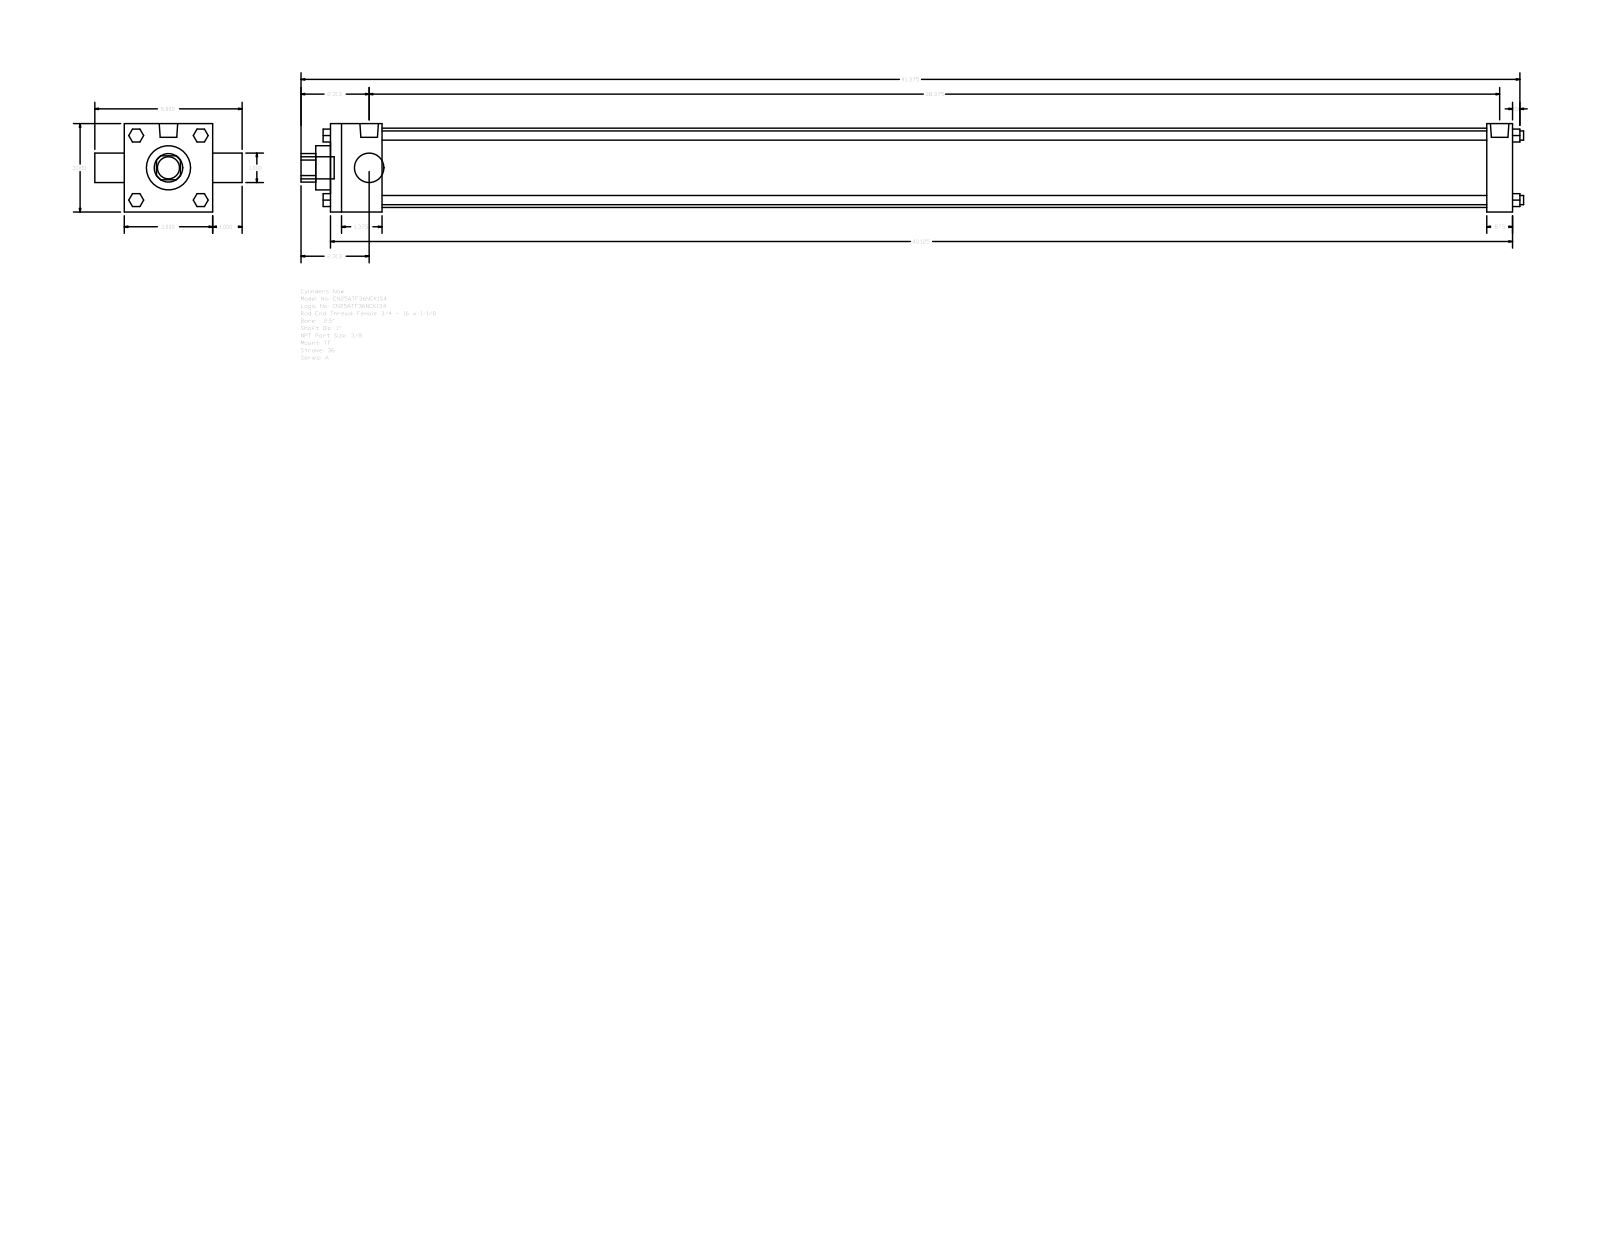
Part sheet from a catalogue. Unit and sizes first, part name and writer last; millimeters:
Units: millimetres
Overall size (bounding box): 1054.1 × 127 × 76.2
Round holes (diameter × count): ⌀25.4 ×2, ⌀38.1 ×1, ⌀68.33 ×1
Round bosses / shafts (diameter × count): ⌀7.94 ×4, ⌀5.56 ×3, ⌀15.93 ×2, ⌀19.05 ×1
Partial cylindrical surfaces — rounded edges, fillets, slot ends (radius × count): R12.29 ×1
Main face-to-face distances: 76.2, 1019.18, 44.45, 996.95, 952.5, 974.73, 22.23, 25.4, 101.6, 12.7
Bodies: 0 solids, 120 faces (92 planar, 28 cylindrical, 0 other)
Part name (STEP PRODUCT): A_TF__0250_1
STEP written by: GSSL Pune (CONFIG_CONTROL_DESIGN)
